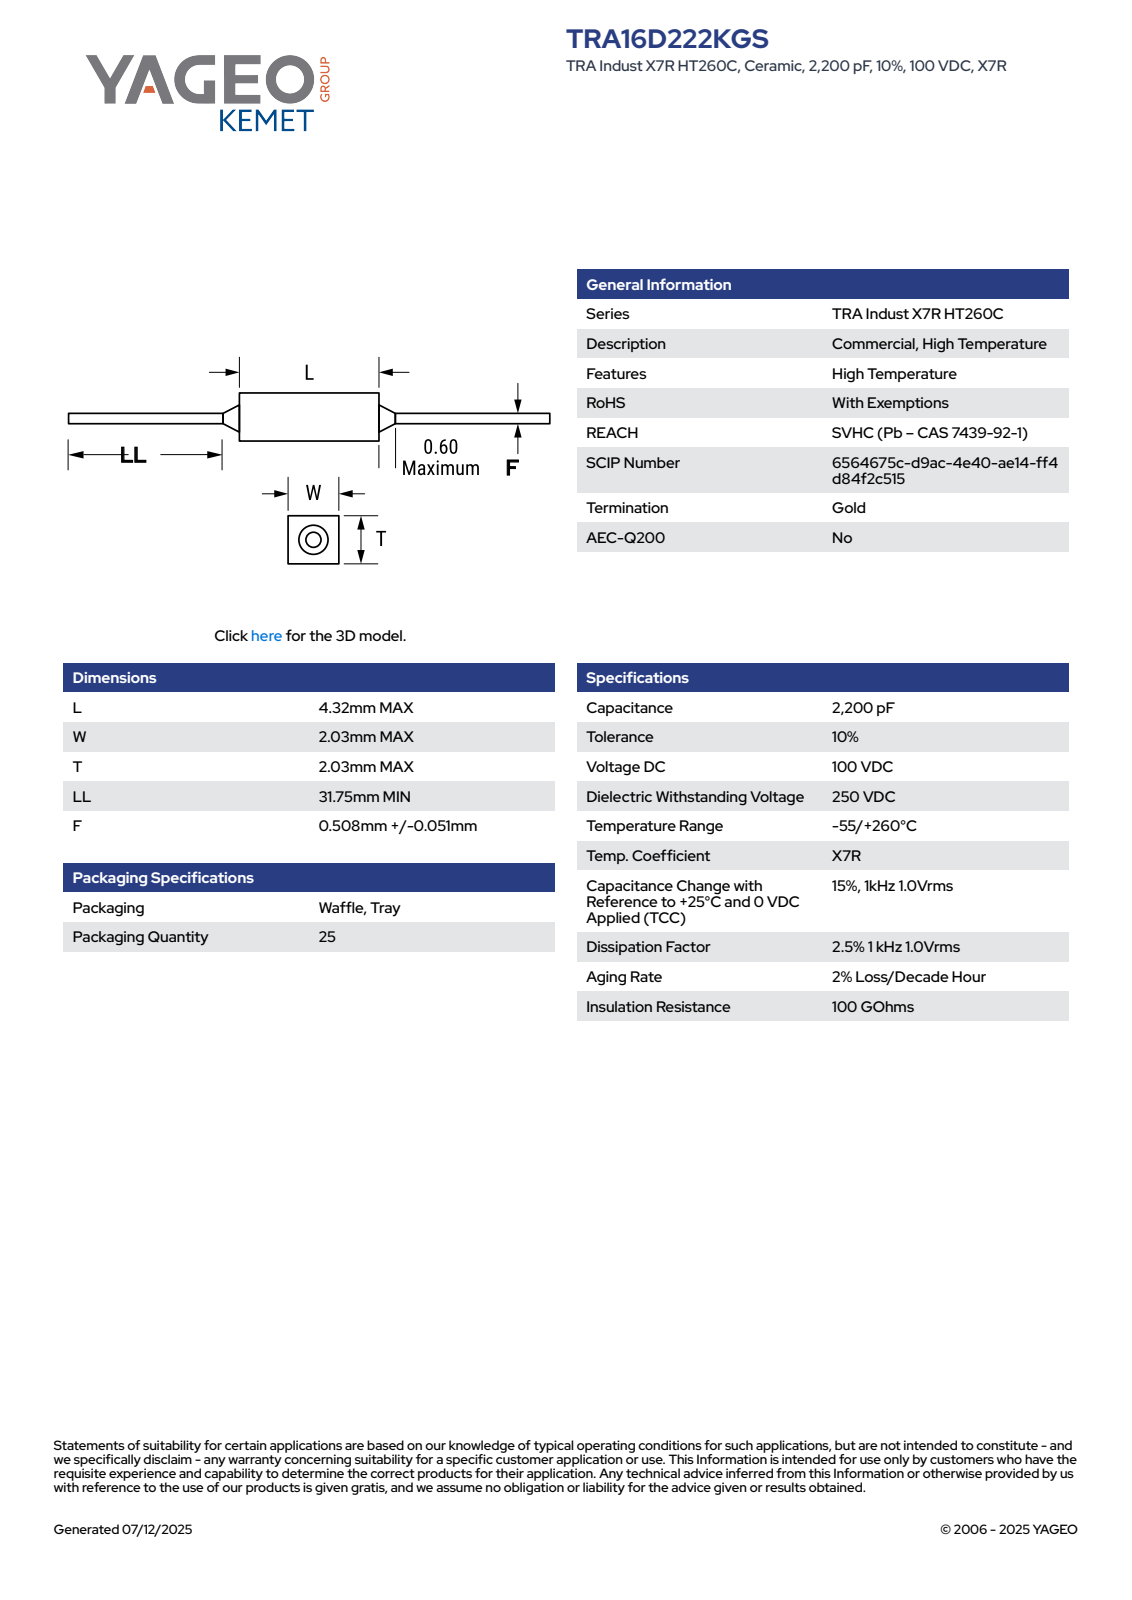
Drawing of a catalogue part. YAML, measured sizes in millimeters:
part_name: "CCR_C3_16_L4.32T2.03LL31.75F0.559W2.03"
step_written_by: "SolidWorks 2021 (AUTOMOTIVE_DESIGN)"
units: millimeters
bodies: {solids: 4, faces: 73, planar: 65, cylindrical: 4, other: 4}
overall_size: [69.02, 2.03, 2.03]
volume: 34
surface_area: 158
round_bosses_or_shafts:
  - {diameter: 0.56, count: 1}
face_to_face_distances: [2.03, 2.02, 4.32, 32.35, 36.67, 69.02, 0.83, 1.2, 0.79, 0.41]
